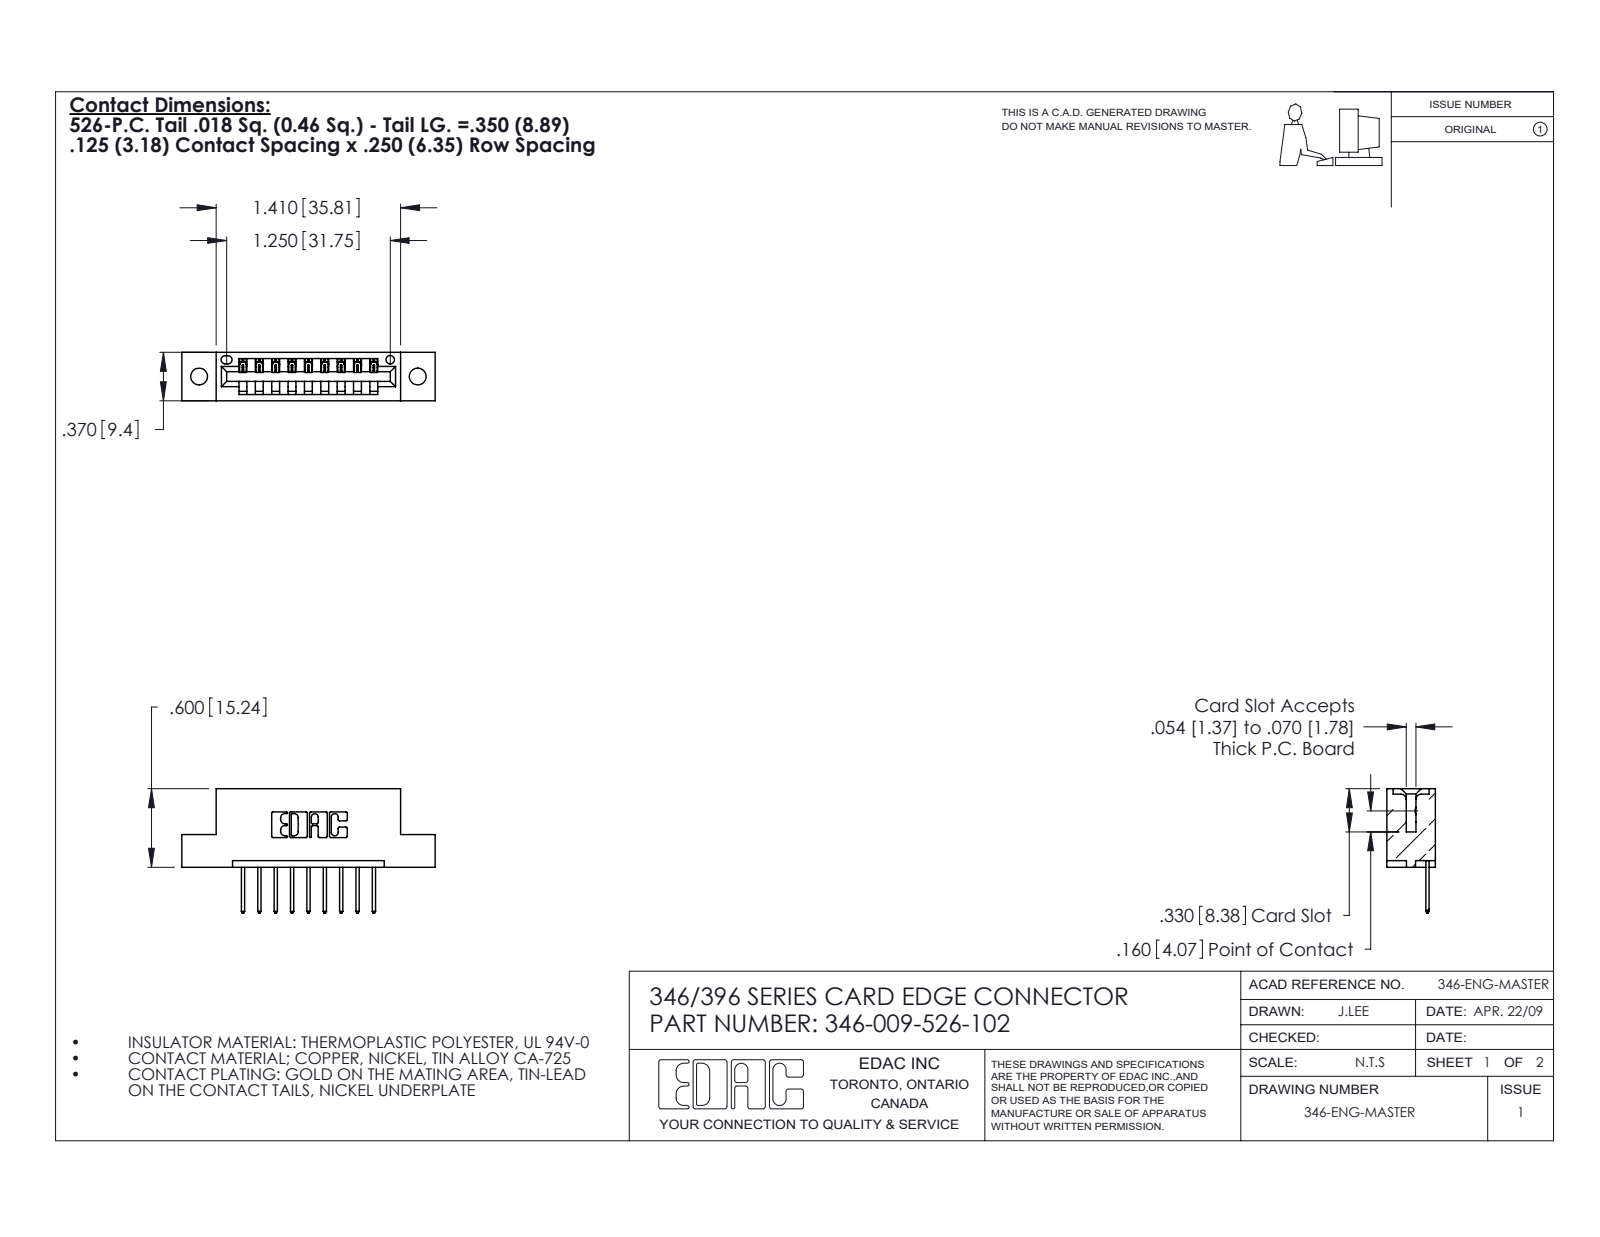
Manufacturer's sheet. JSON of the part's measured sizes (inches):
{"part_name": "346 Part_Flush Mounting Lugs - 0.128 Dia; 345-292-001_345-293-126; 346-009-526-102", "step_written_by": "SolidWorks 2020 (CONFIG_CONTROL_DESIGN)", "units": "inches", "bodies": {"solids": 10, "faces": 644, "planar": 436, "cylindrical": 208, "other": 0}, "overall_size": [1.935, 0.95, 0.37], "volume_in3": 0.271, "surface_area_in2": 7.603, "round_holes": [[0.128, 2], [0.064, 1]], "partial_cylinders_radius": [[0.01, 22], [0.006, 18], [0.01, 18], [0.007, 6], [0.031, 6], [0.026, 3], [0.031, 2], [0.04, 2]], "face_to_face_distances": [0.25, 0.37, 0.048, 0.322, 0.072, 0.298, 0.025, 0.148, 0.222, 0.1], "hole_center_spacings": [0.246, 1.465, 1.67]}
